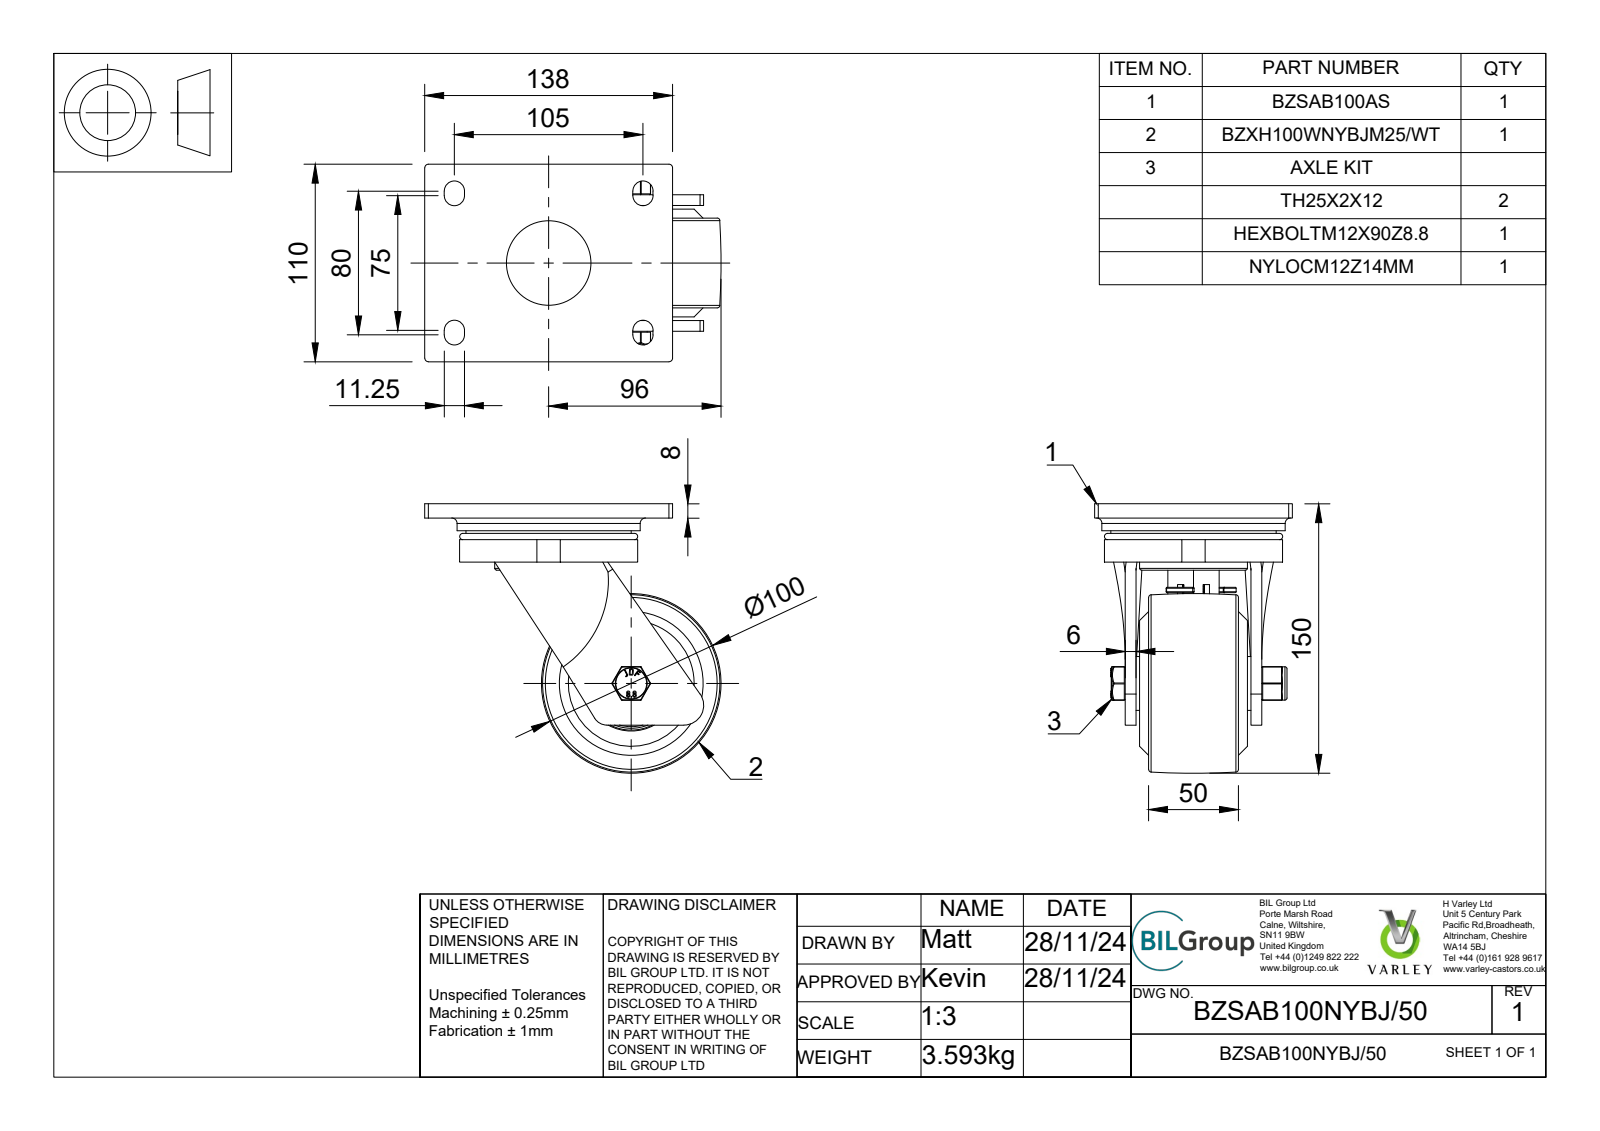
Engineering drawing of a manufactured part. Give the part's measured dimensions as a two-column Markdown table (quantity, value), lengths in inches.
| quantity | value |
| --- | --- |
| part name | BZSAB100NYBJ/50 v4; BZSAB100AS v1; FABRICATED STEEL TOP PLATE; FABRICATED STEEL TOP PLATE Geometry (+8 more) |
| STEP written by | Autodesk Translation Framework v13.20.0.188 (AP242_MANAGED_MODEL_BASED_3D_ENGINEERING_MIM_LF) |
| units | inches |
| bodies | 42 solids, 1272 faces (465 planar, 235 cylindrical, 572 other) |
| overall size | 6.496 × 5.906 × 4.331 |
| volume | 47.64 in³ |
| surface area | 308.7 in² |
| round holes (diameter × count) | 0.157 × 1, 0.217 × 1, 0.472 × 1, 0.488 × 1, 0.492 × 1, 0.551 × 1, 0.709 × 1, 0.984 × 1, 1.024 × 1, 1.352 × 1, 1.367 × 1, 1.428 × 1 |
| round bosses / shafts (diameter × count) | 4.016 × 1, 3.937 × 1, 3.622 × 1, 2.362 × 1, 1.8 × 1, 1.743 × 1, 1.386 × 1, 1.271 × 1 |
| partial cylindrical surfaces (radius × count) | 0.02 × 50, 0.221 × 8, 0.01 × 6, 0.019 × 4, 0.035 × 4, 0.079 × 4, 0.035 × 2, 0.035 × 2 |
| main face-to-face distances | 0.315, 2.756, 0.236, 1.28, 0.079, 0.197, 0.276, 1.181, 0.669, 1.772 |
| hole center spacings | 0.787, 2.733 |
